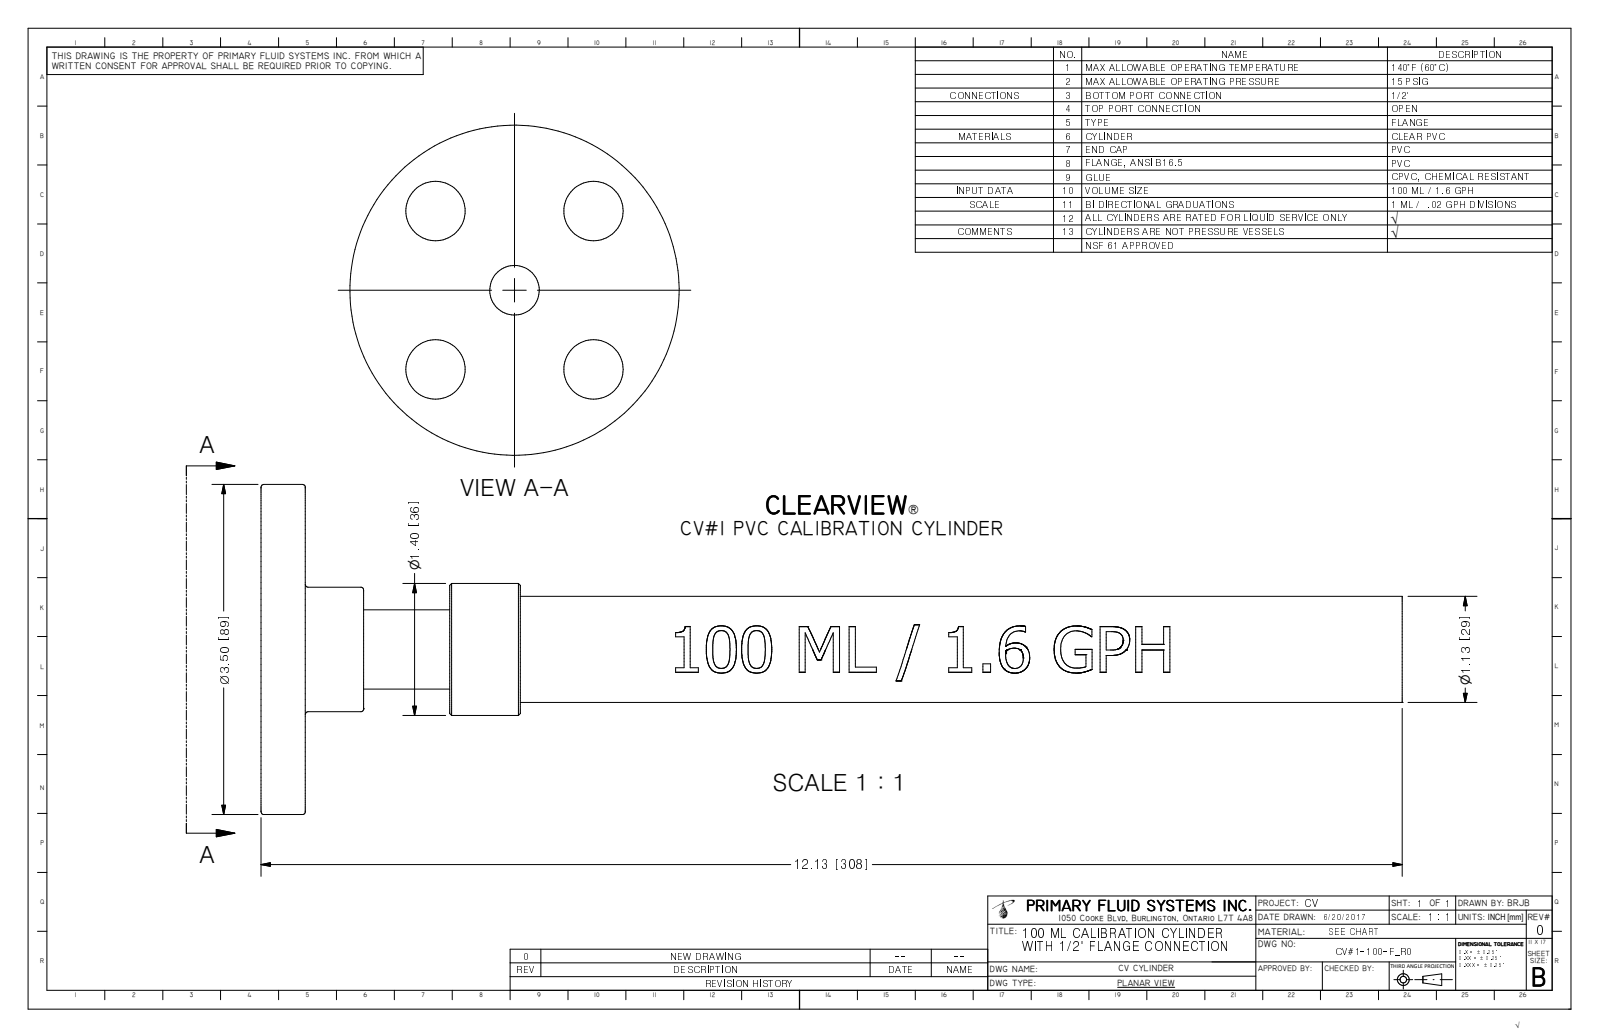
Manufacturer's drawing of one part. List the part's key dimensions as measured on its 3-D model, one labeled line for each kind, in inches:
Part name (STEP PRODUCT): PV#1-100-F_R0
STEP written by: Autodesk Inventor 2009 (AUTOMOTIVE_DESIGN)
Units: inches
Bodies: 2 solids, 243 faces (91 planar, 26 cylindrical, 126 other)
Overall size (bounding box): 12.13 × 3.5 × 3.5
Volume: 7.547 in³ · Surface area: 110.9 in²
Round holes (diameter × count): ⌀0.63 ×4, ⌀0.526 ×1, ⌀1.005 ×1
Round bosses / shafts (diameter × count): ⌀3.5 ×1, ⌀1.4 ×1, ⌀1.32 ×1, ⌀1.125 ×1
Partial cylindrical surfaces — rounded edges, fillets, slot ends (radius × count): R0.561 ×1
Main face-to-face distances: 0.47, 2.005, 1.535, 0.915, 1.09, 0.62, 2.38, 1.91, 1.29, 0.375
Hole centre spacings: 1.188, 1.68, 2.375
